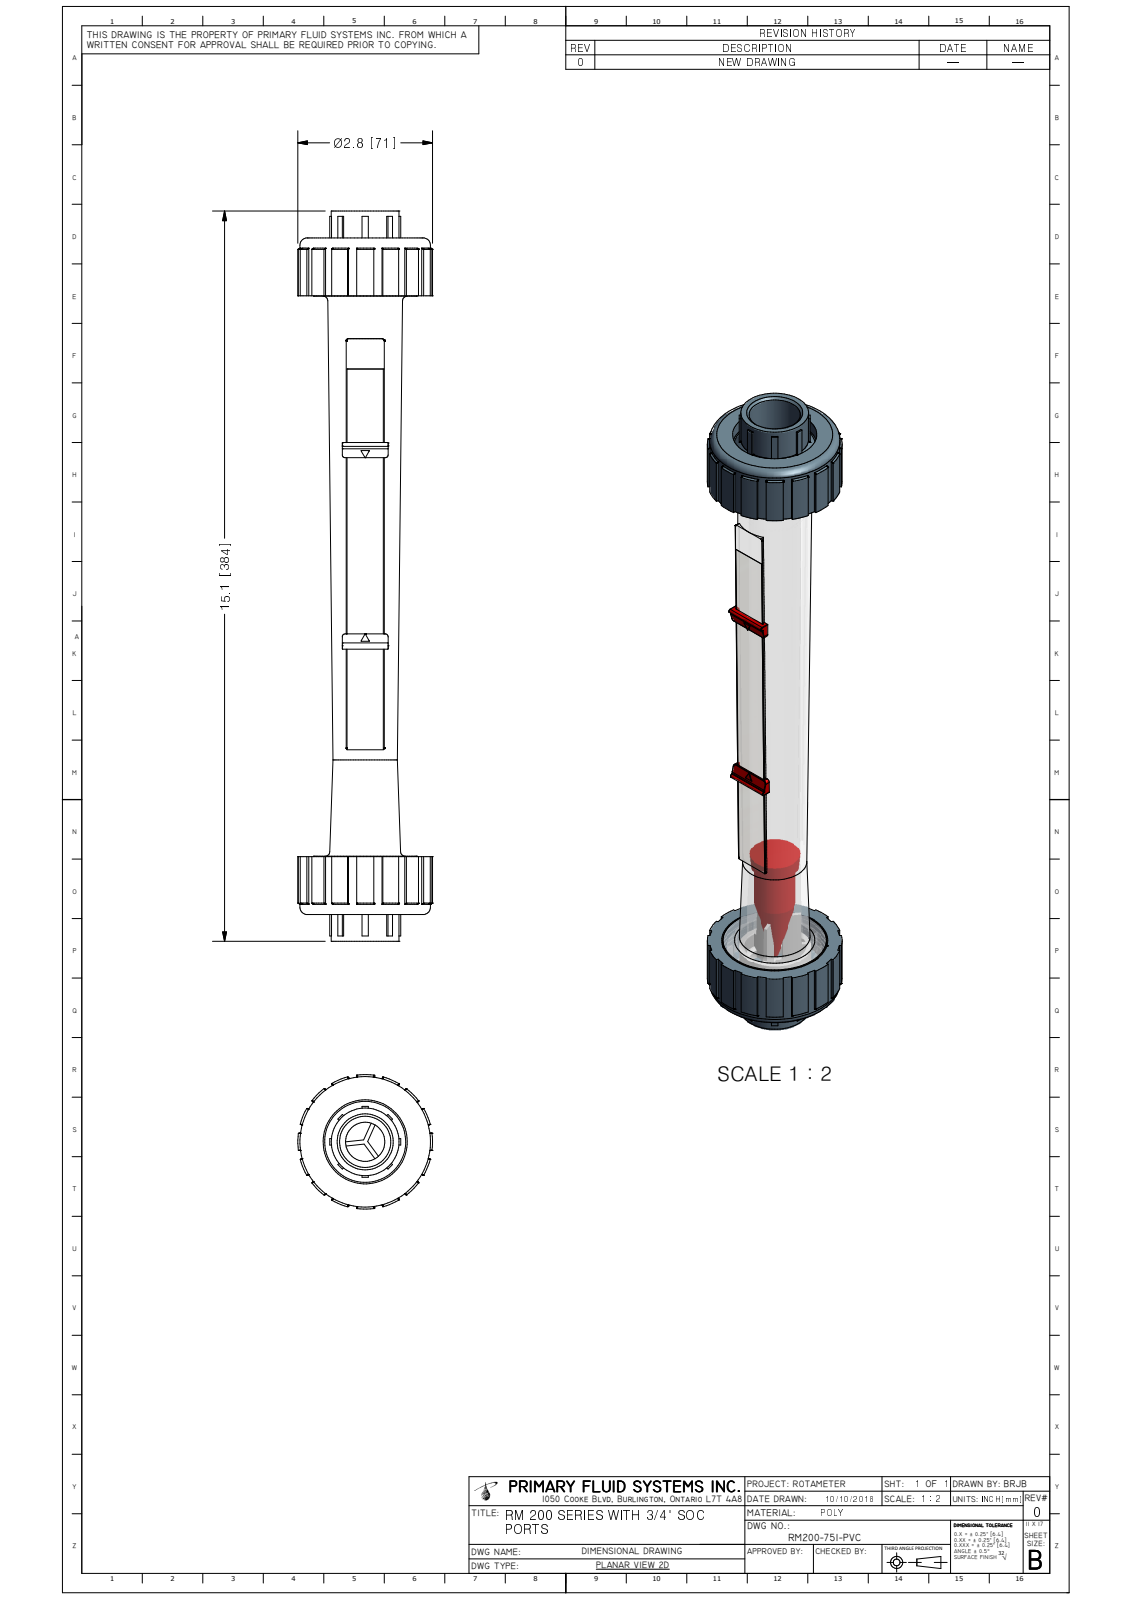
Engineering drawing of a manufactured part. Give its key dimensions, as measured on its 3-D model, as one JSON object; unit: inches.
{"part_name": "RM200-75I-PVC_R0", "step_written_by": "Autodesk Inventor 2009 (AUTOMOTIVE_DESIGN)", "units": "inches", "bodies": {"solids": 1, "faces": 587, "planar": 262, "cylindrical": 126, "other": 199}, "overall_size": [15.1, 2.783, 2.783], "volume_in3": 31.99, "surface_area_in2": 168.3, "round_holes": [[1.058, 1], [1.738, 1], [2.19, 1]], "round_bosses_or_shafts": [[2.697, 1], [2.152, 1], [2.026, 1], [1.485, 1], [1.4, 1]], "partial_cylinders_radius": [[0.008, 18], [0.01, 16], [0.004, 10], [0.006, 4], [0.06, 4], [0.008, 2], [0.04, 2], [0.045, 2]], "face_to_face_distances": [1.197, 12.795, 1.205, 12.787, 11.59, 0.496, 13.496, 0.701, 12.299, 12.291]}
